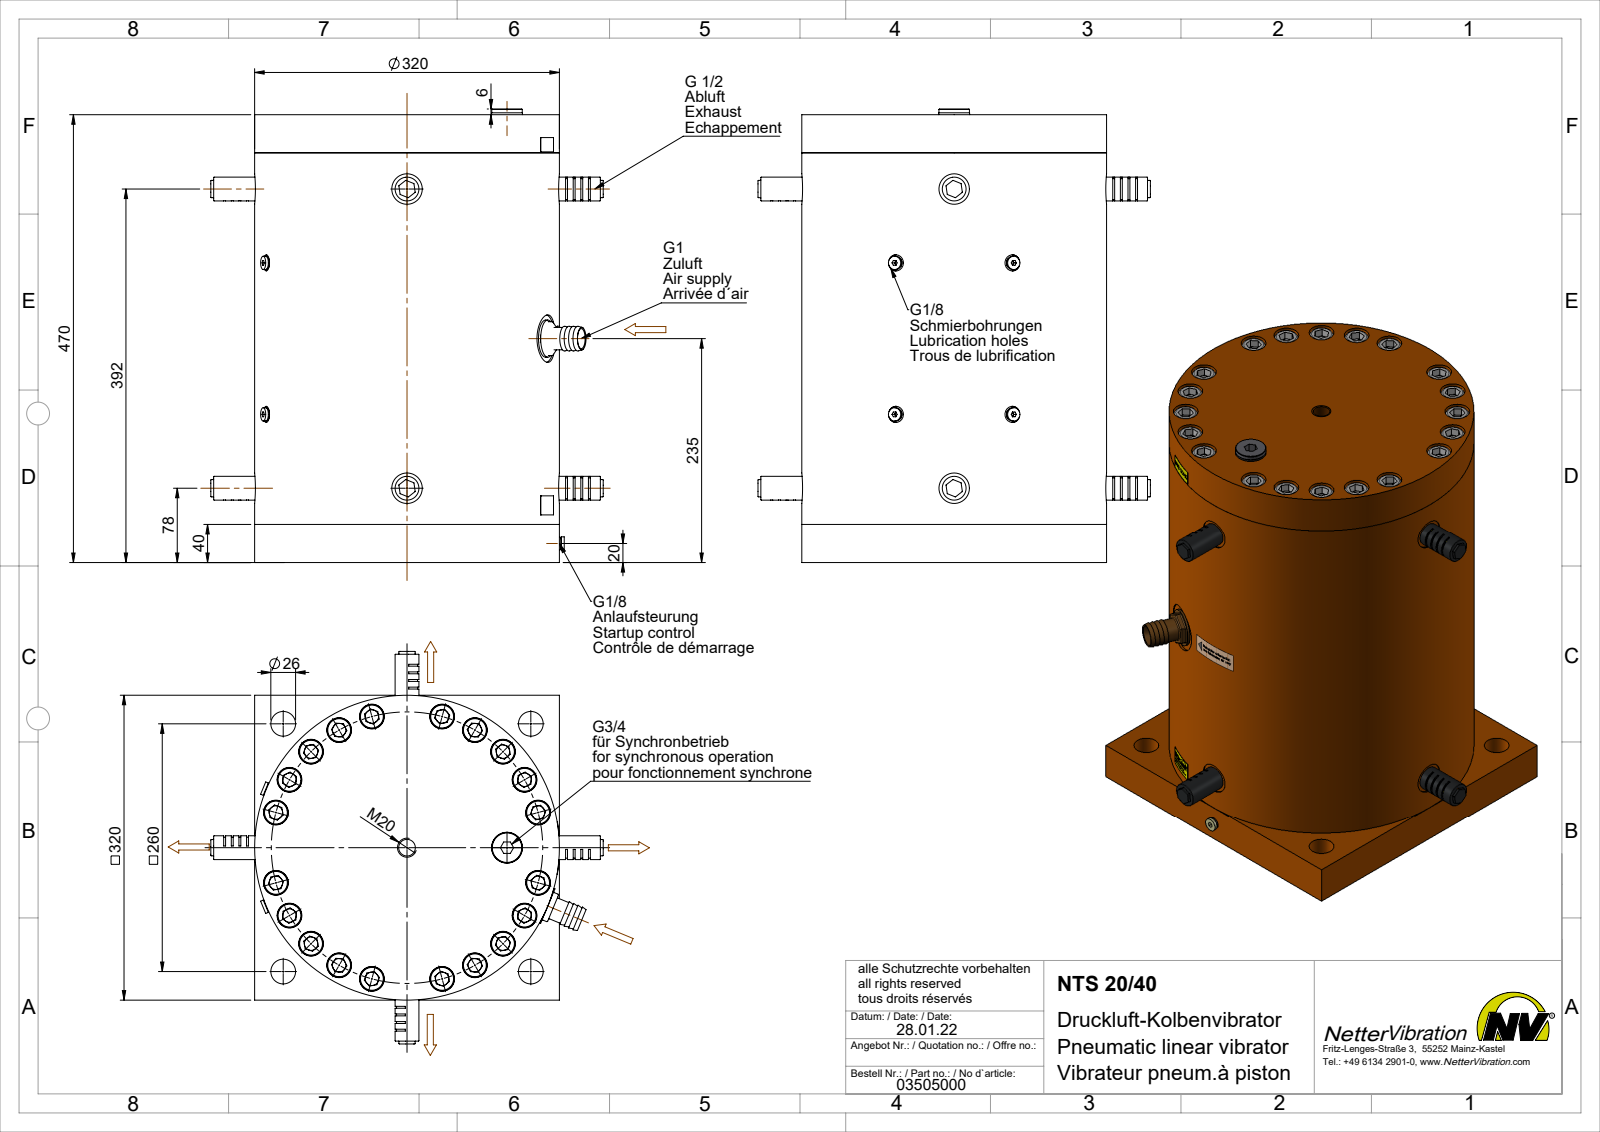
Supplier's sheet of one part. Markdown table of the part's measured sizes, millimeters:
| quantity | value |
| --- | --- |
| part name | NTS 20-40 Kolbenvibrator #03505000 |
| STEP written by | SolidWorks 2015 (AUTOMOTIVE_DESIGN) |
| units | millimeters |
| bodies | 107 solids, 7482 faces (5546 planar, 1246 cylindrical, 690 other) |
| overall size | 476 × 412 × 412 |
| volume | 38 440 000 mm³ |
| surface area | 1 522 000 mm² |
| round holes (diameter × count) | 17 × 24, 26 × 24, 14 × 20, 2 × 6, 10 × 6, 6 × 5, 8.57 × 5, 18.63 × 4, 32 × 4, 17.5 × 1, 21 × 1, 24.12 × 1 |
| round bosses / shafts (diameter × count) | 25.4 × 20, 24 × 20, 16 × 20, 14 × 5, 13 × 5, 9.73 × 5, 25 × 4, 22 × 4 |
| partial cylindrical surfaces (radius × count) | 0.5 × 156, 1 × 18, 160.2 × 1 |
| main face-to-face distances | 390, 40, 430, 39, 429, 469, 1, 470, 320, 409 |
| hole center spacings | 142.5, 37.2, 109.06, 226.1, 263.3, 282.56, 73.76, 201.52 |
